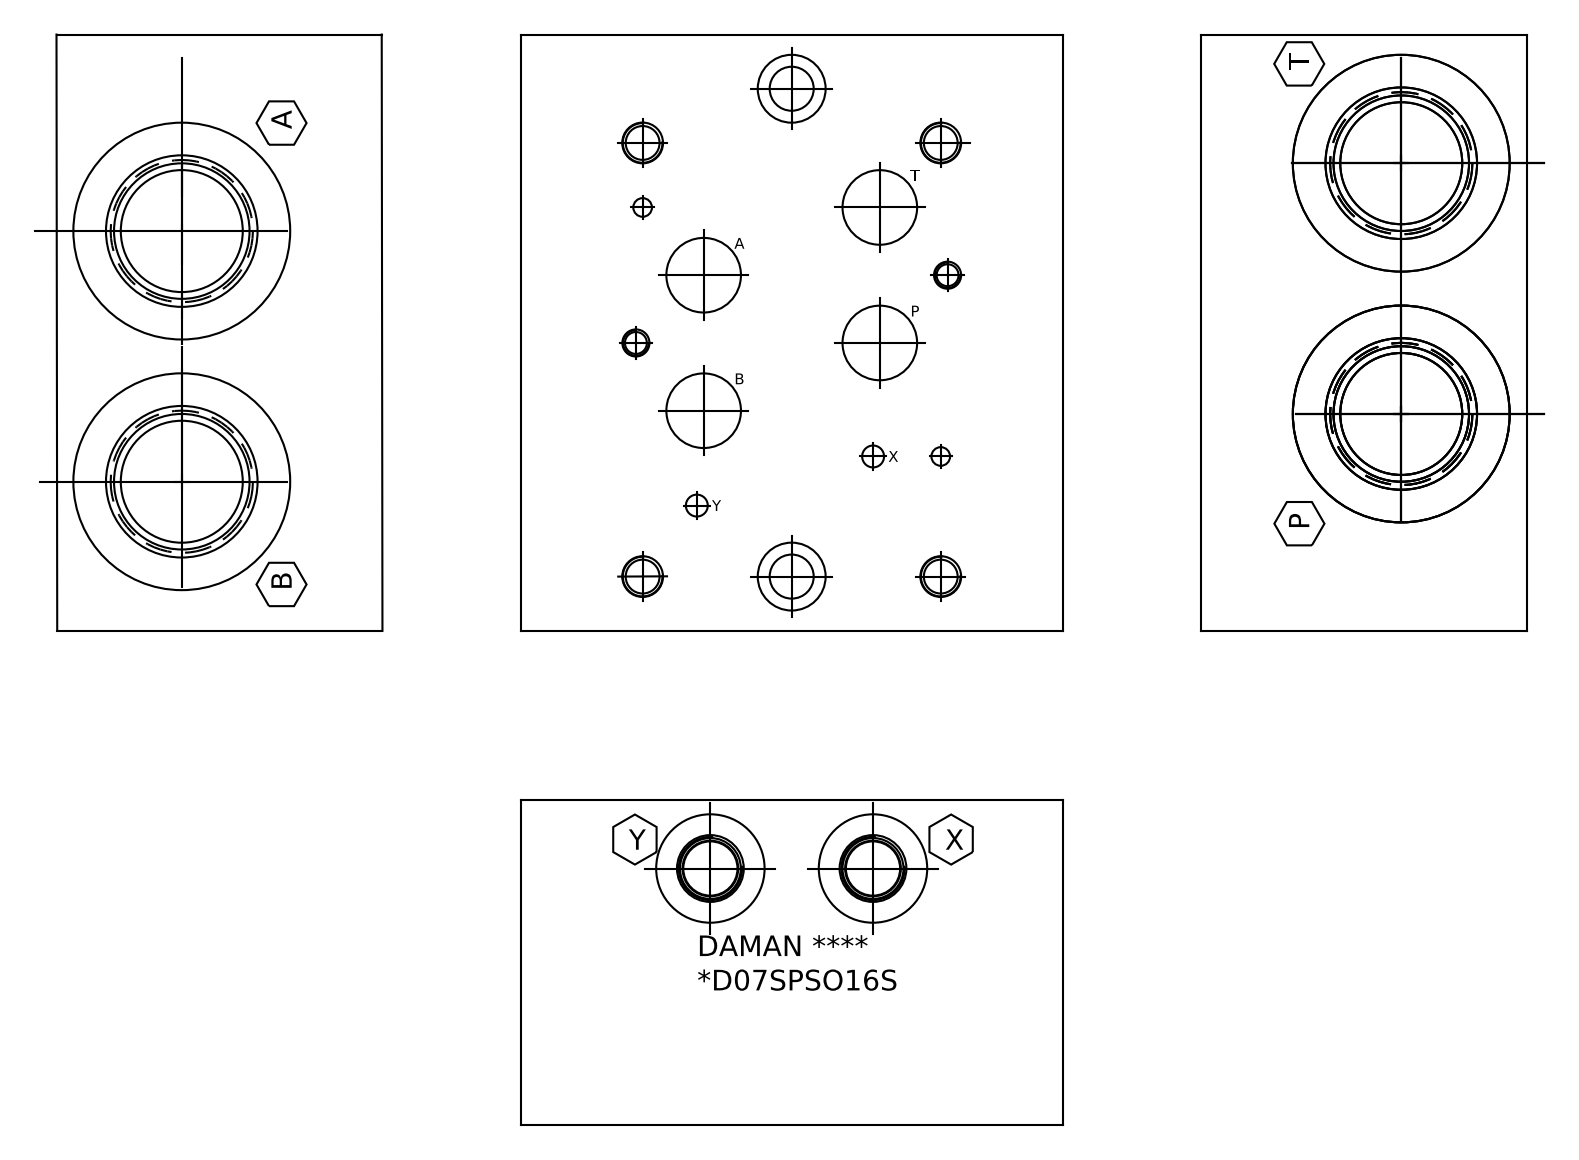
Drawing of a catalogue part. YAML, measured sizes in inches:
part_name: "Part_AD07SPSO16S_3D"
step_written_by: "Autodesk Inventor 2019 (AUTOMOTIVE_DESIGN)"
units: inches
bodies: {solids: 1, faces: 546, planar: 308, cylindrical: 56, other: 182}
overall_size: [5.5, 5, 3]
volume: 72.86
surface_area: 160.1
round_holes:
  - {diameter: 0.25, count: 4}
  - {diameter: 0.312, count: 4}
  - {diameter: 0.375, count: 4}
  - {diameter: 0.688, count: 4}
  - {diameter: 1.125, count: 4}
  - {diameter: 1.231, count: 4}
  - {diameter: 1.329, count: 4}
  - {diameter: 1.934, count: 4}
  - {diameter: 0.172, count: 2}
  - {diameter: 0.201, count: 2}
  - {diameter: 0.406, count: 2}
  - {diameter: 0.484, count: 2}
face_to_face_distances: [3, 5.5, 5, 0.031, 4.969, 4.938, 5.469, 0.75, 0.781, 4.219]
hole_center_spacings: [1.741, 0.624, 0.884, 0.884, 1.25, 1.688, 2.25, 2.312]
